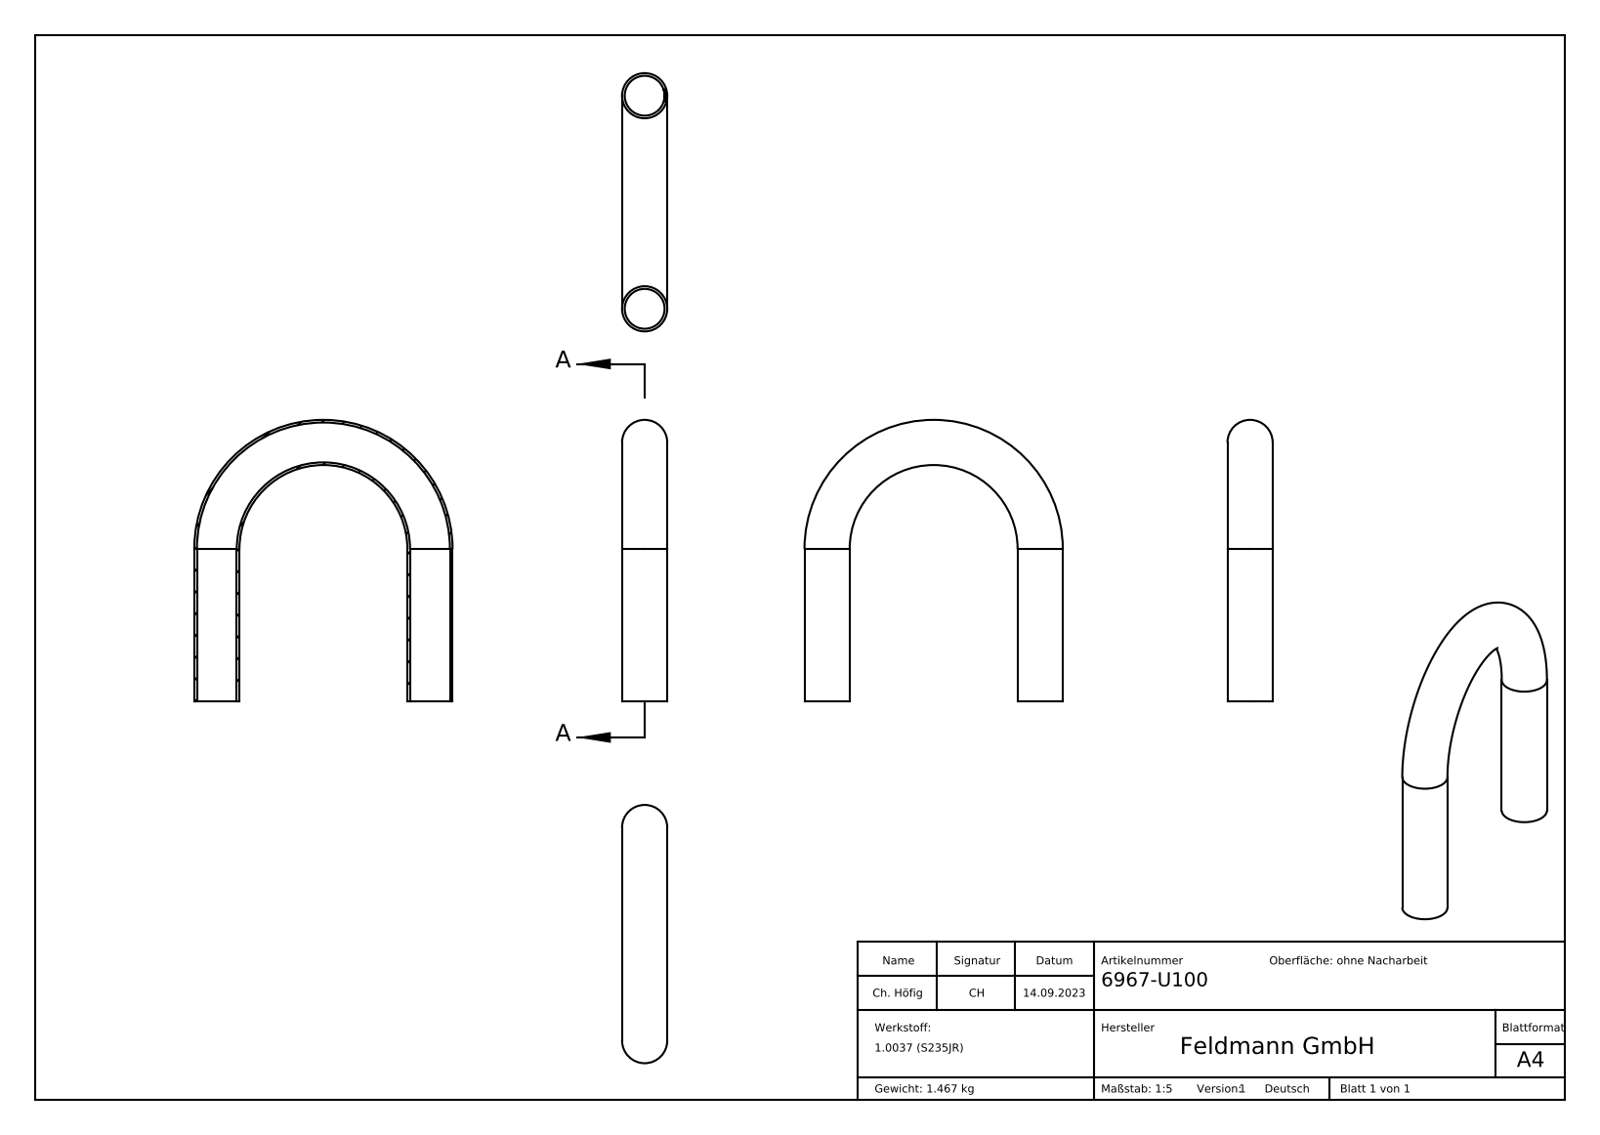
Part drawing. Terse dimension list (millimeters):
name: 6967-U100
written by: SolidWorks 2018 (CONFIG_CONTROL_DESIGN)
unit: mm
bodies: 1 solid, 218 faces (112 planar, 4 cylindrical, 102 other)
size: 264.12 × 242.4 × 42.4
volume: 188 024 mm³; area: 151 052 mm²
holes: 2× ⌀37.4
bosses: 2× ⌀42.4
face distances: 0.44, 0.4, 0.36, 0.32, 0.47, 0.51, 0.39, 0.52, 0.79, 1.75
hole spacings: 200
